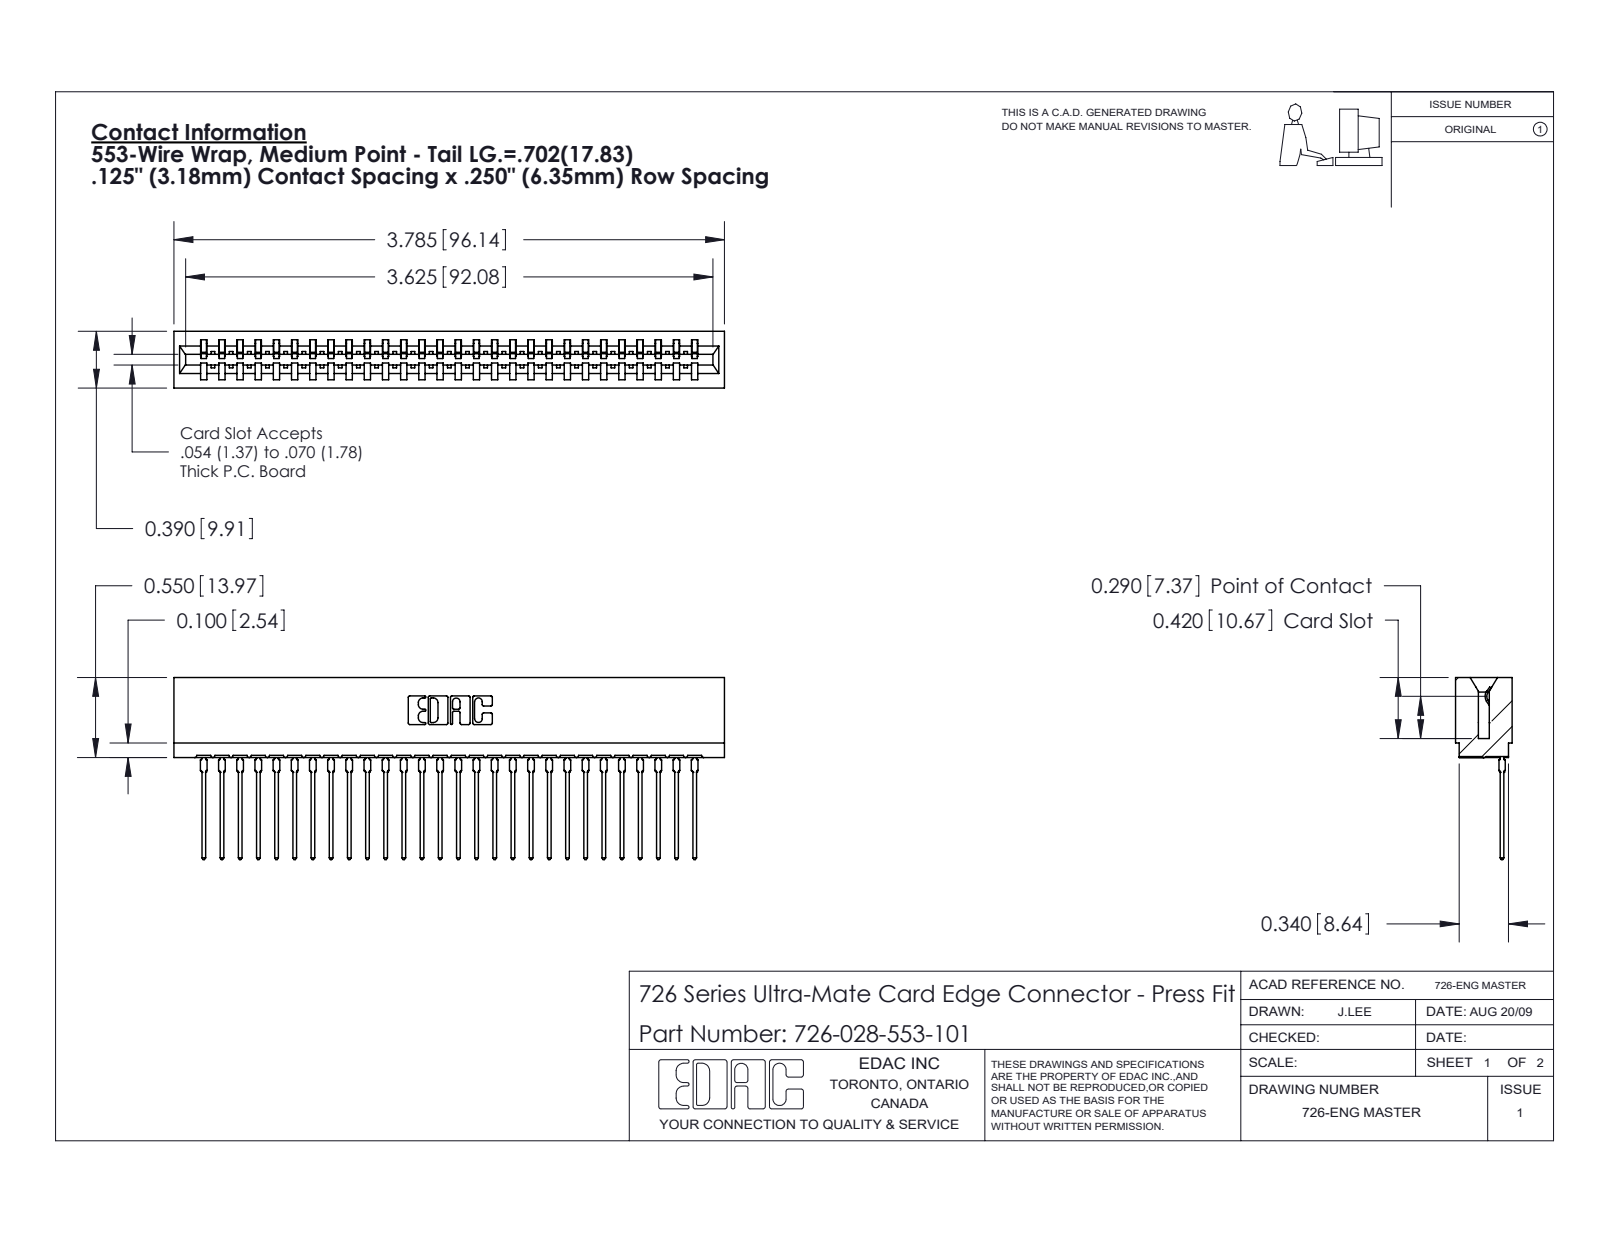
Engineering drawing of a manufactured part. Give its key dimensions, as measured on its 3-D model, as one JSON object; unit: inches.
{"part_name": "746-292-001_553; 726 Part_.515 Slot Depth - 01; 726-028-553-101", "step_written_by": "SolidWorks 2020 (CONFIG_CONTROL_DESIGN)", "units": "inches", "bodies": {"solids": 29, "faces": 3121, "planar": 1819, "cylindrical": 574, "other": 728}, "overall_size": [3.785, 1.251, 0.39], "volume_in3": 0.535, "surface_area_in2": 21.23, "partial_cylinders_radius": [[0.021, 56], [0.015, 29], [0.01, 22], [0.007, 6], [0.031, 6], [0.005, 4], [0.011, 4], [0.026, 3]], "face_to_face_distances": [0.057, 0.333, 0.39, 0.25, 0.025, 0.307, 0.083, 0.275, 0.5, 0.365]}
